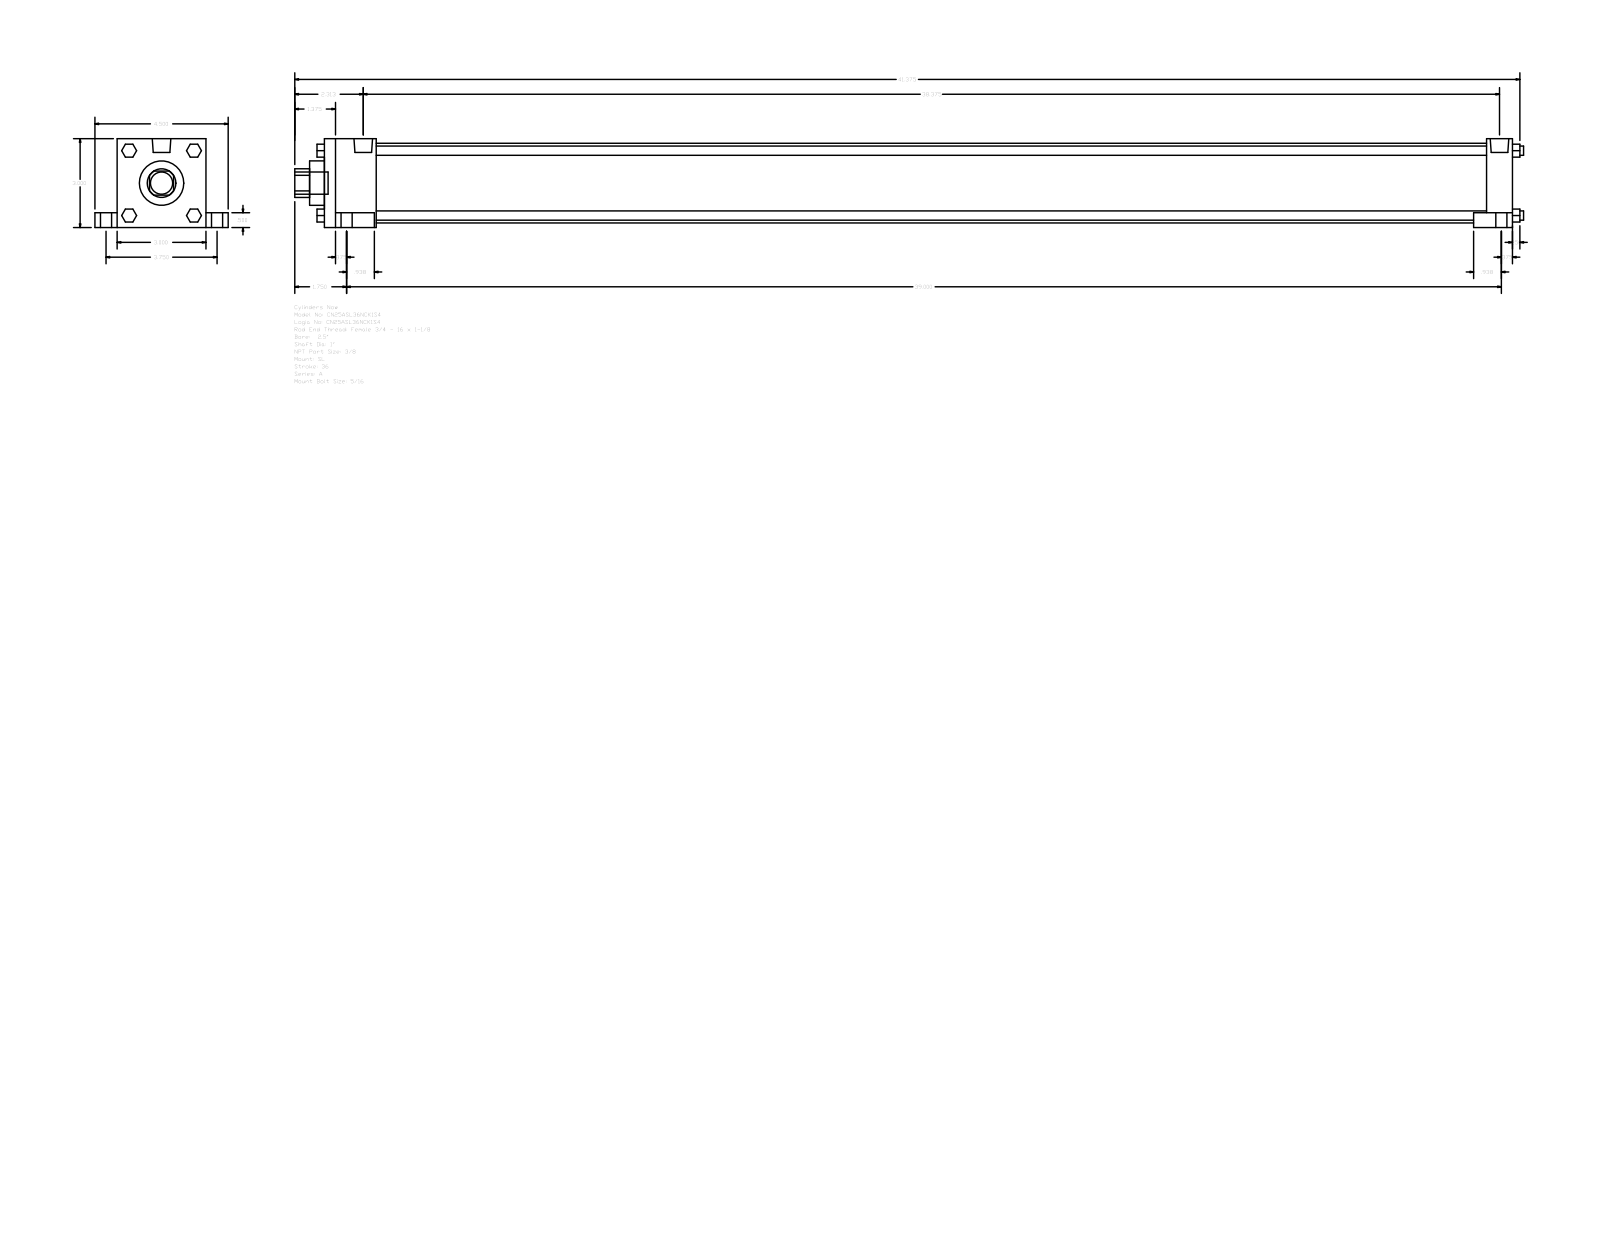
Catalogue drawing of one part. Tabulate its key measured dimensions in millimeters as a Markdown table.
| quantity | value |
| --- | --- |
| part name | A_SL__0250_1 |
| STEP written by | GSSL Pune (CONFIG_CONTROL_DESIGN) |
| units | millimeters |
| bodies | 0 solids, 148 faces (112 planar, 36 cylindrical, 0 other) |
| overall size | 1054.1 × 114.3 × 76.2 |
| round holes (diameter × count) | 25.4 × 1, 38.1 × 1, 68.33 × 1 |
| round bosses / shafts (diameter × count) | 15.88 × 4, 9.53 × 4, 7.94 × 4, 5.56 × 4, 15.93 × 2, 19.05 × 1 |
| partial cylindrical surfaces (radius × count) | 12.29 × 1 |
| main face-to-face distances | 76.2, 1019.18, 12.7, 44.45, 974.73, 996.95, 952.5, 22.23, 19.05, 63.5 |
